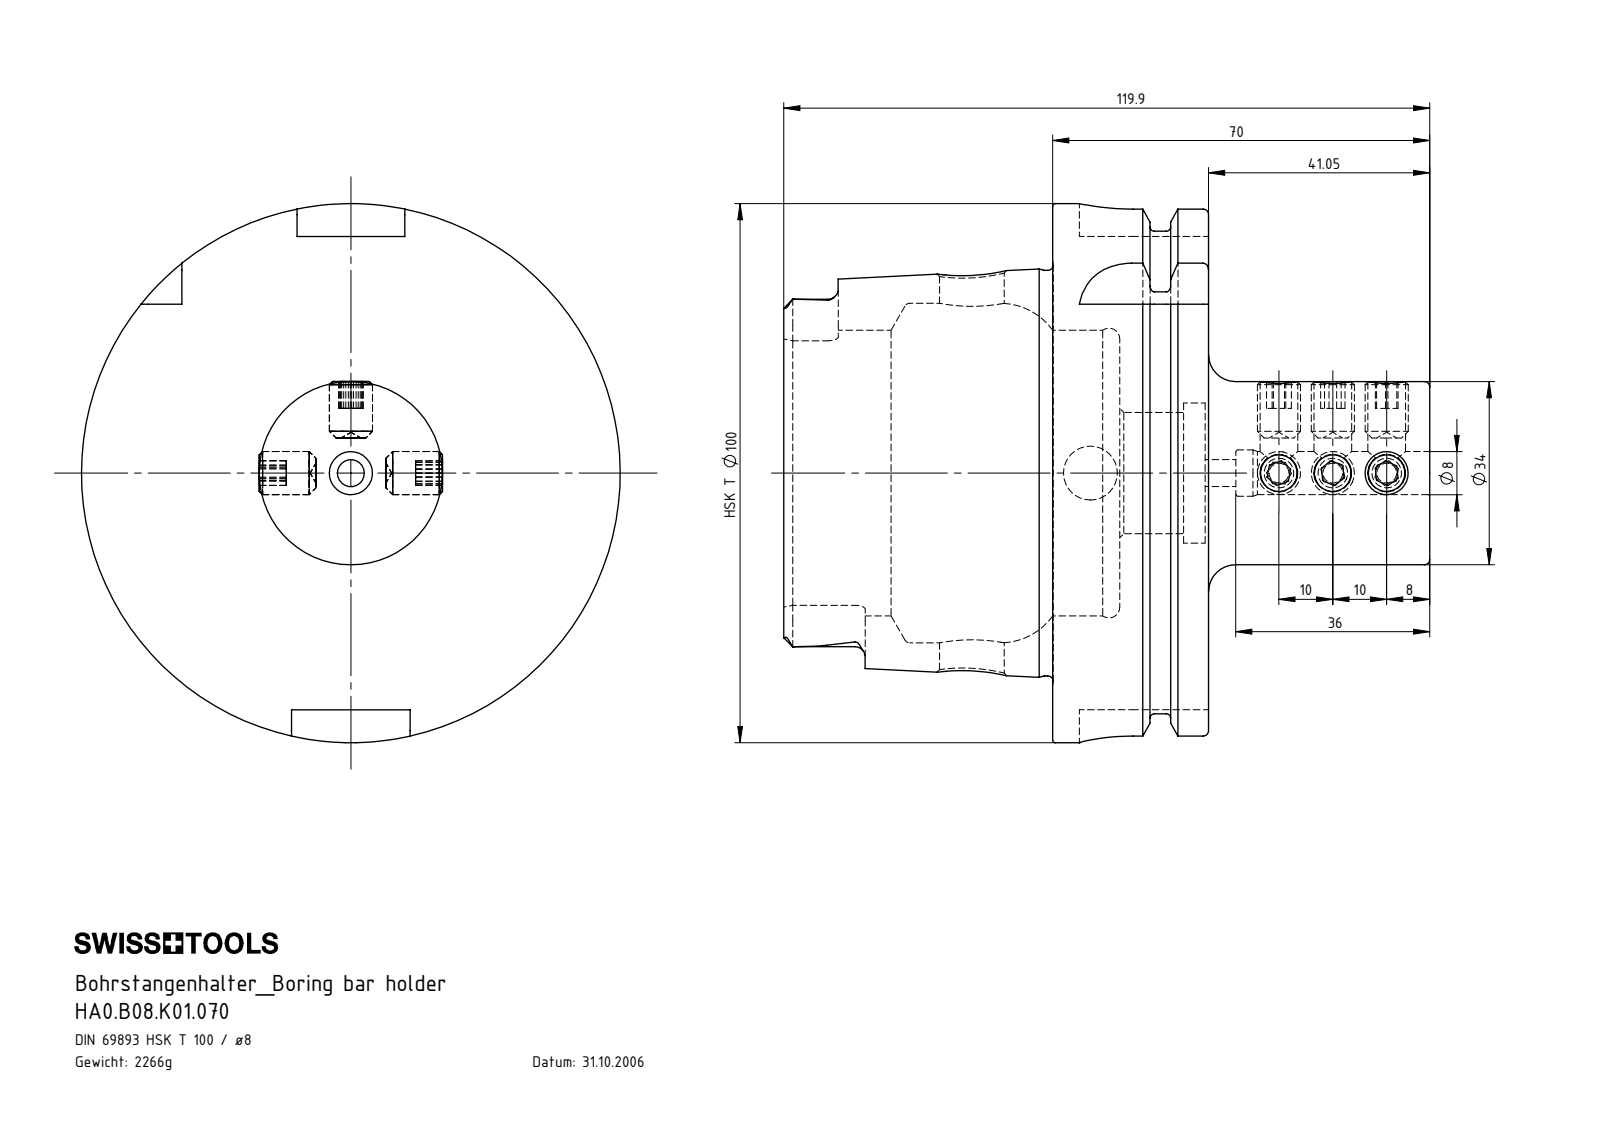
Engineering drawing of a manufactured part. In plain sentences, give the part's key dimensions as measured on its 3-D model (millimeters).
The part is named "HA0.B08.K01.070; W08-ER1.001.010_Default; HA0-B08.K01.070_A_Fertigbearbeitung". Its 3-D file was written by "SolidWorks 2011 (AUTOMOTIVE_DESIGN)". It is 10 solids with 334 faces: 122 planar, 89 cylindrical and 123 other. Overall it measures 119.9 by 100 by 100 millimeters. Its volume is 288 679 cubic millimeters and its surface area 60 325 square millimeters. Round holes: 6 of diameter 7, 1 of diameter 5, 1 of diameter 8, 1 of diameter 8.6, 1 of diameter 10, 1 of diameter 12, 1 of diameter 22.5, 1 of diameter 26, 1 of diameter 53, 1 of diameter 63. Round bosses or shafts: 6 of diameter 8, 1 of diameter 100, 1 of diameter 91.95, 1 of diameter 75.26, 1 of diameter 34. Partial cylindrical surfaces (rounded edges, fillets, slot ends): 6 of radius 1.9, 4 of radius 10, 2 of radius 4.83, 2 of radius 4.88. The main face-to-face distances are 28.95, 16.5, 12.45, 49.9, 62.35, 78.85, 119.9, 70, 57.55, 41.05. The hole center spacings are 10, 20, 35, 45, 55, 57, 67, 77.
